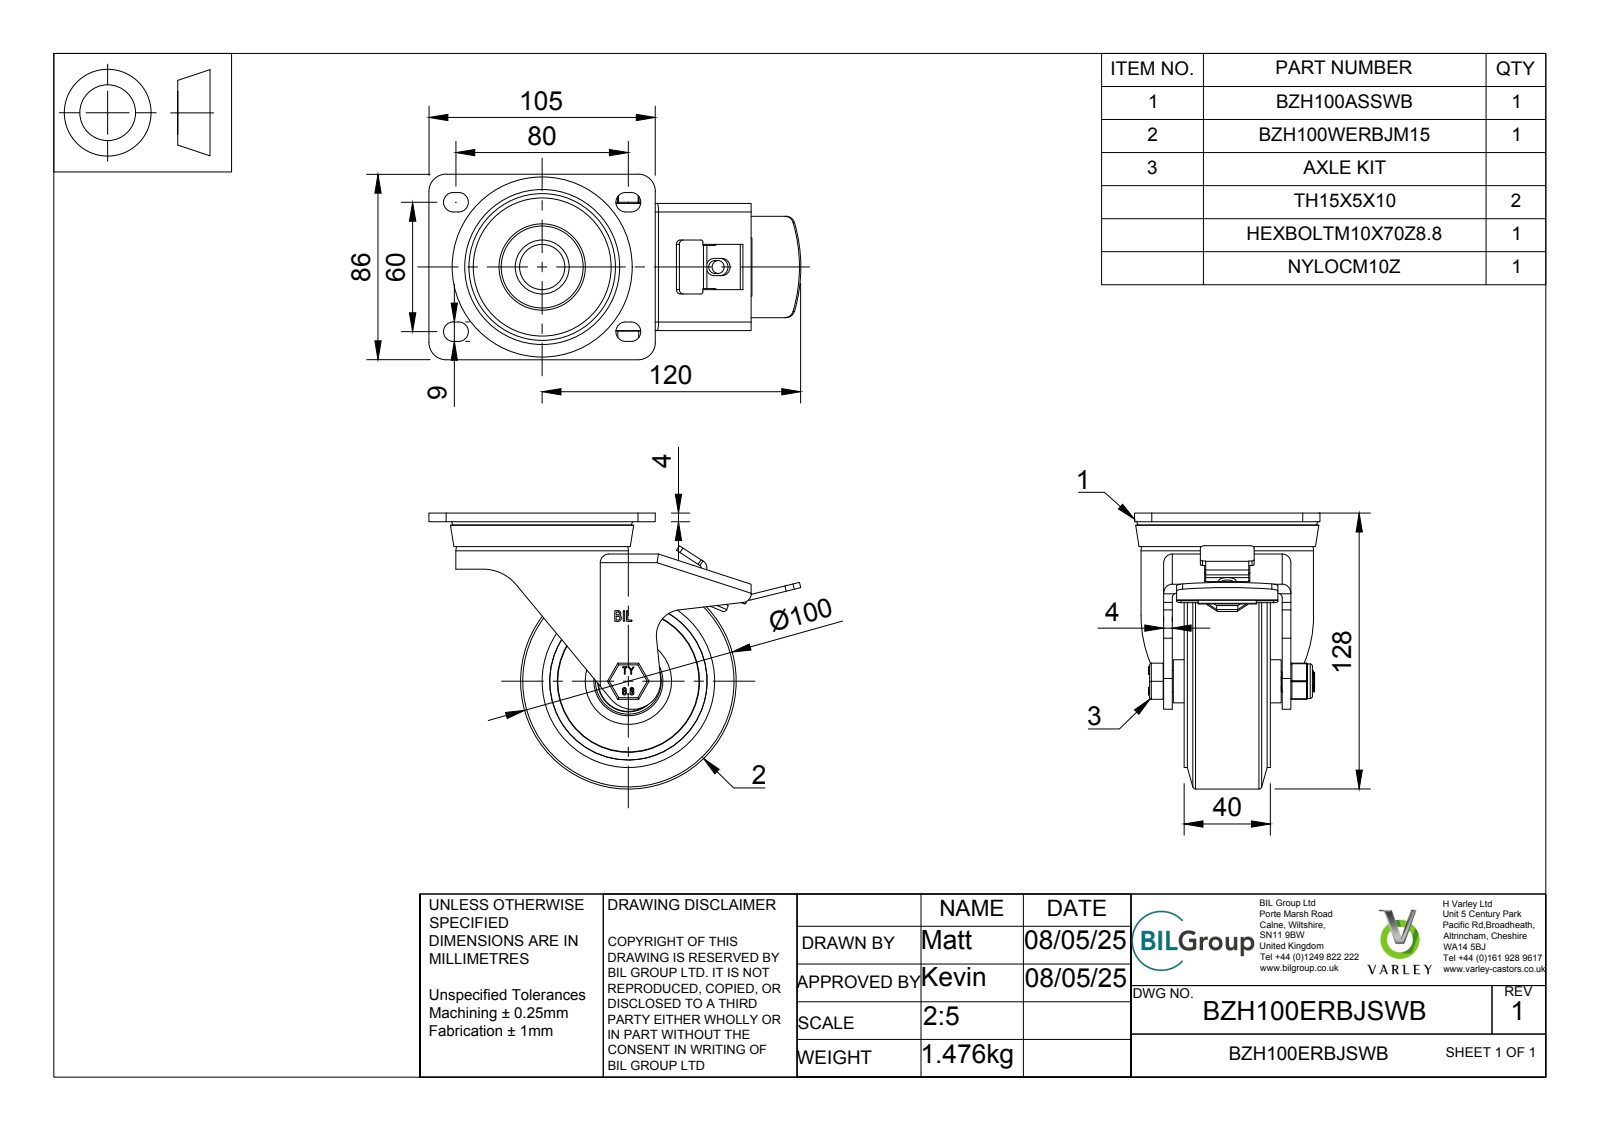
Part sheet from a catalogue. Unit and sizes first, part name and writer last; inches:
Units: inches
Overall size (bounding box): 6.791 × 5.039 × 3.386
Round holes (diameter × count): ⌀1.26 ×2, ⌀0.236 ×1, ⌀0.394 ×1, ⌀0.402 ×1, ⌀0.413 ×1, ⌀0.472 ×1, ⌀0.591 ×1, ⌀0.709 ×1, ⌀0.787 ×1, ⌀0.827 ×1, ⌀0.984 ×1, ⌀1.079 ×1
Round bosses / shafts (diameter × count): ⌀3.15 ×2, ⌀3.937 ×1, ⌀2.362 ×1, ⌀1.575 ×1, ⌀1.22 ×1, ⌀1.118 ×1, ⌀1.102 ×1, ⌀0.85 ×1
Partial cylindrical surfaces — rounded edges, fillets, slot ends (radius × count): R0.02 ×27, R0.079 ×18, R0.157 ×10, R0.177 ×8, R0.03 ×6, R0.059 ×6, R0.315 ×4, R0.039 ×3
Main face-to-face distances: 0.157, 0.846, 1.004, 0.295, 0.374, 0.945, 0.039, 0.217, 0.453, 1.949
Volume: 23.33 in³ · Surface area: 256.5 in²
Bodies: 42 solids, 1326 faces (632 planar, 273 cylindrical, 421 other)
Part name (STEP PRODUCT): BZH100ERBJSWB v3; BZH100ASSWB v1; ZINC PLATED, PRESSED STEEL TOP PLATE; ZINC PLATED, PRESSED STEEL FORKS (+8 more)
STEP written by: Autodesk Translation Framework v14.4.0.0 (AUTOMOTIVE_DESIGN)
